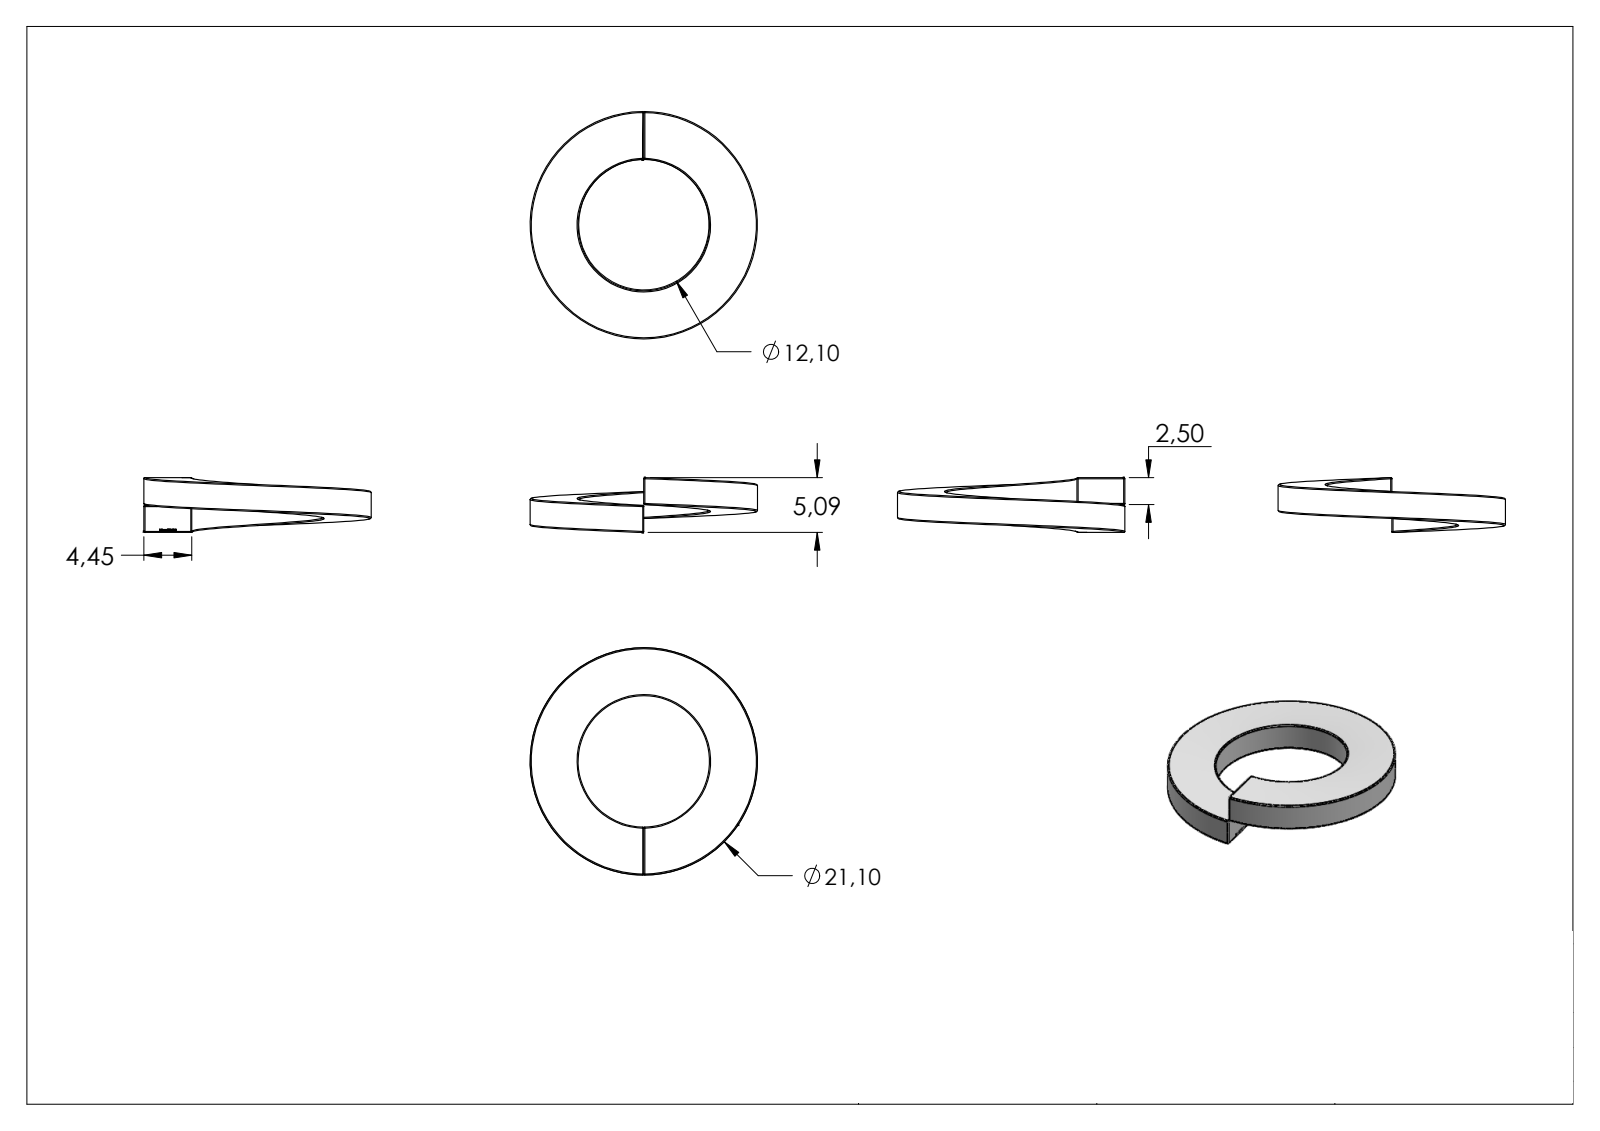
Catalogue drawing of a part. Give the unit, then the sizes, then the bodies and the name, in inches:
Units: inches
Overall size (bounding box): 0.831 × 0.831 × 0.201
Main face-to-face distances: 0.019, 0.038, 0.019, 0.039, 0.051, 0.032, 0.02, 0.057, 0.013, 0.044
Volume: 0.036 in³ · Surface area: 1.15 in²
Bodies: 1 solid, 284 faces (141 planar, 0 cylindrical, 143 other)
Part name (STEP PRODUCT): 58319-240-12
STEP written by: SolidWorks 2015 (CONFIG_CONTROL_DESIGN)
